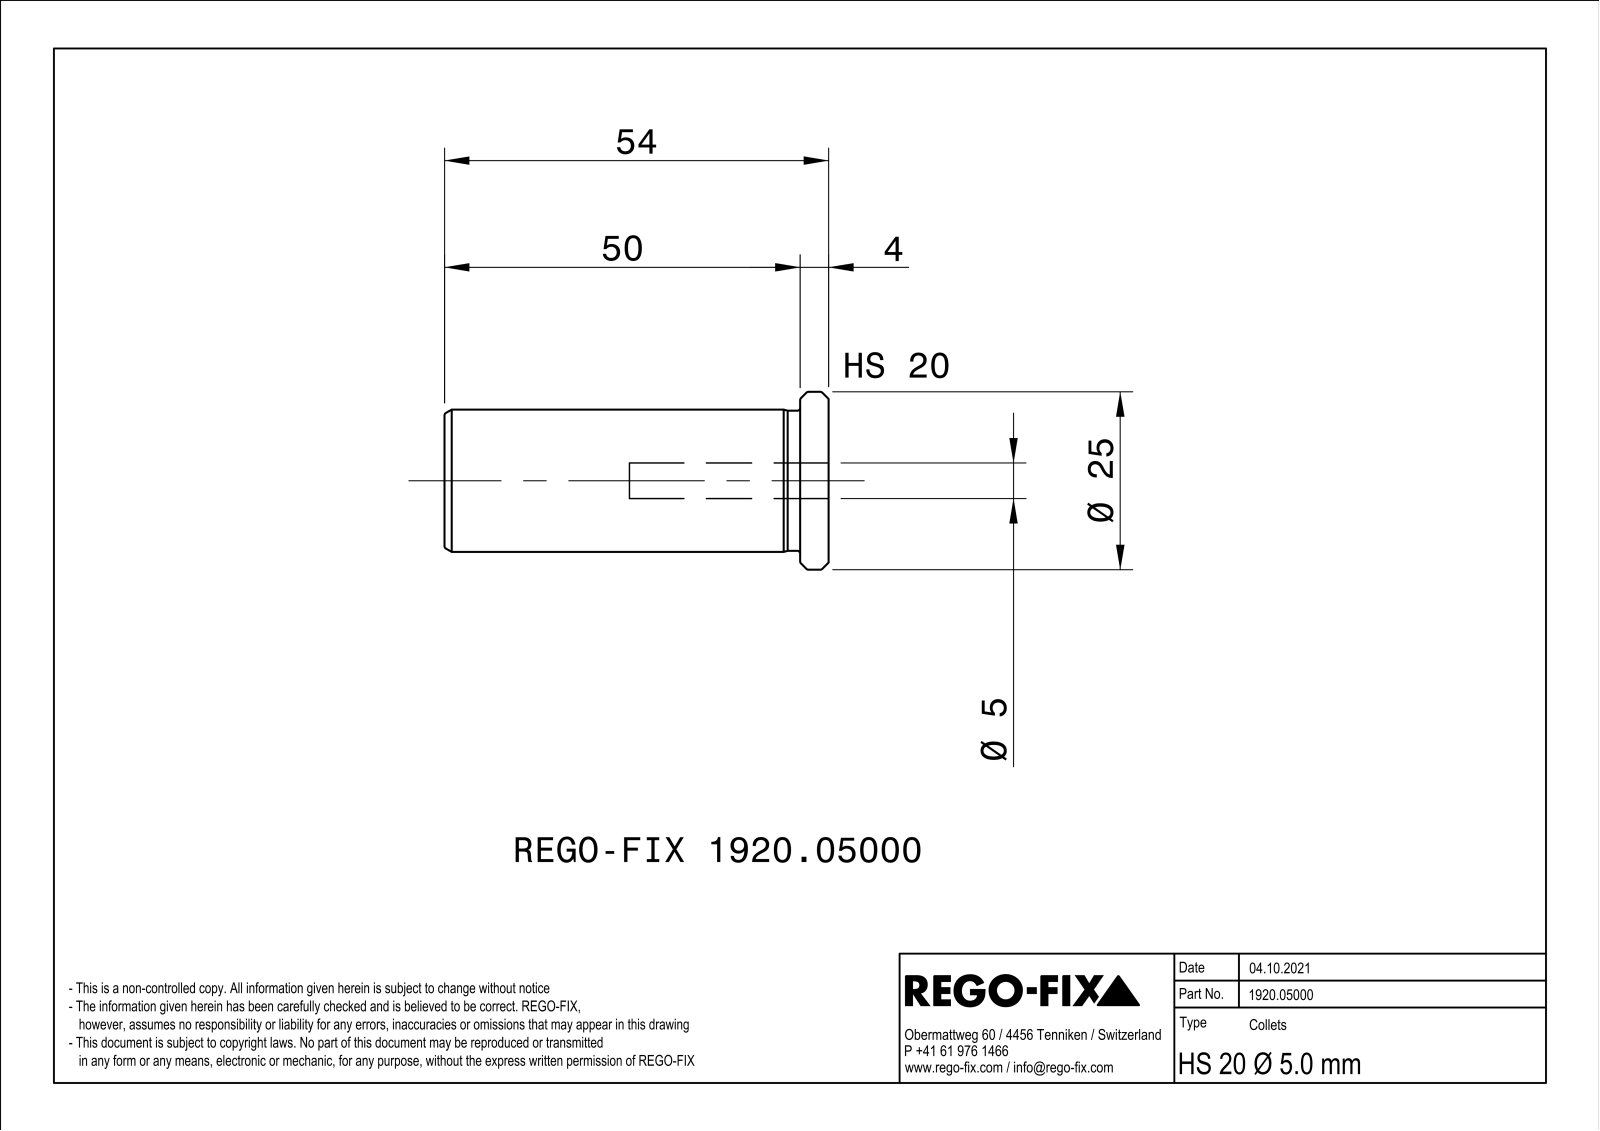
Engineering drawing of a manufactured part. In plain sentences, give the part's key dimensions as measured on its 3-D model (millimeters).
The part is named "NOCUT". Its 3-D file was written by "SIEMENS PLM Software Solid Edge ST10 (AUTOMOTIVE_DESIGN)". It is 1 solid with 73 faces: 22 planar, 12 cylindrical and 39 other. Overall it measures 54 by 24.99 by 24.99 millimeters. Its volume is 12 918 cubic millimeters and its surface area 7 134 square millimeters. Round holes: 1 of diameter 5, 1 of diameter 10, 1 of diameter 16.5. Round bosses or shafts: 1 of diameter 25, 1 of diameter 20, 1 of diameter 19.7. The main face-to-face distances are 0.8, 4, 54, 50.
